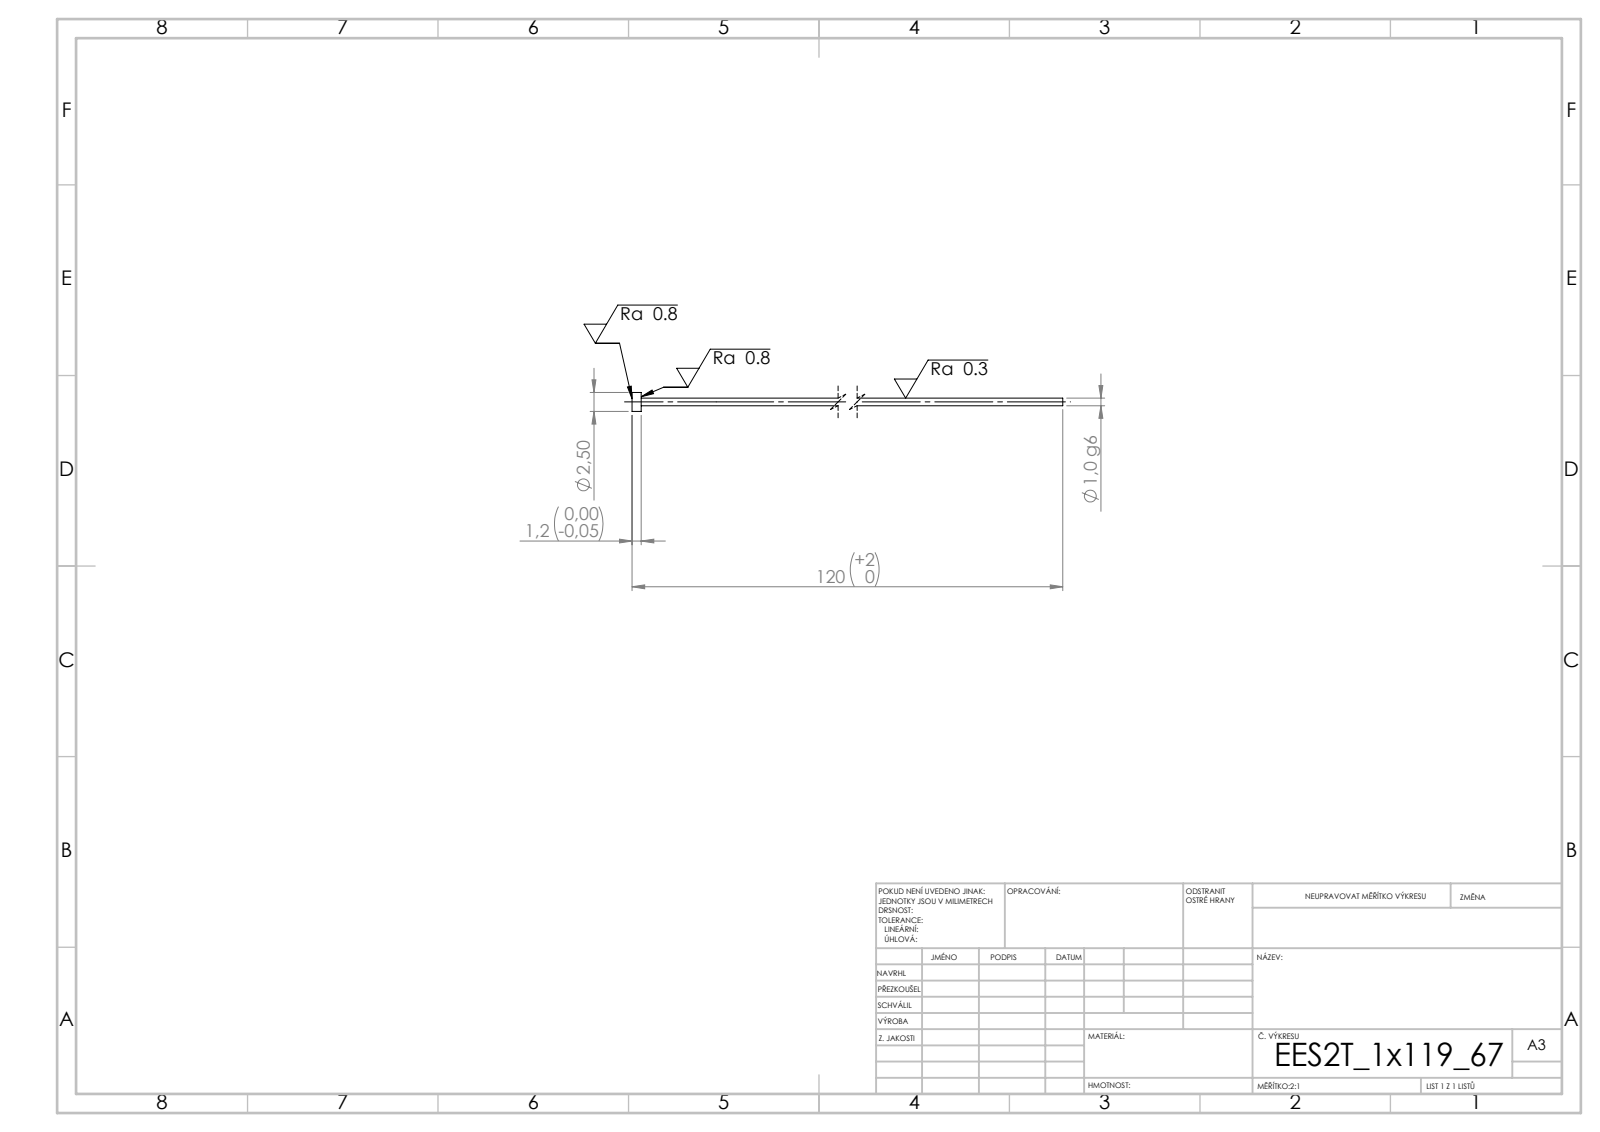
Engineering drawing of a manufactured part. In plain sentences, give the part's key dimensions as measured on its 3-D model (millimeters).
Its 3-D file was written by "SolidWorks 2019 (CONFIG_CONTROL_DESIGN)". It is 1 solid with 7 faces: 3 planar, 4 cylindrical and 0 other. Overall it measures 119.67 by 2.5 by 2.5 millimeters. Its volume is 99 cubic millimeters and its surface area 391 square millimeters. Round bosses or shafts: 1 of diameter 2.5, 1 of diameter 1. The main face-to-face distances are 1.2, 119.67, 118.47.
